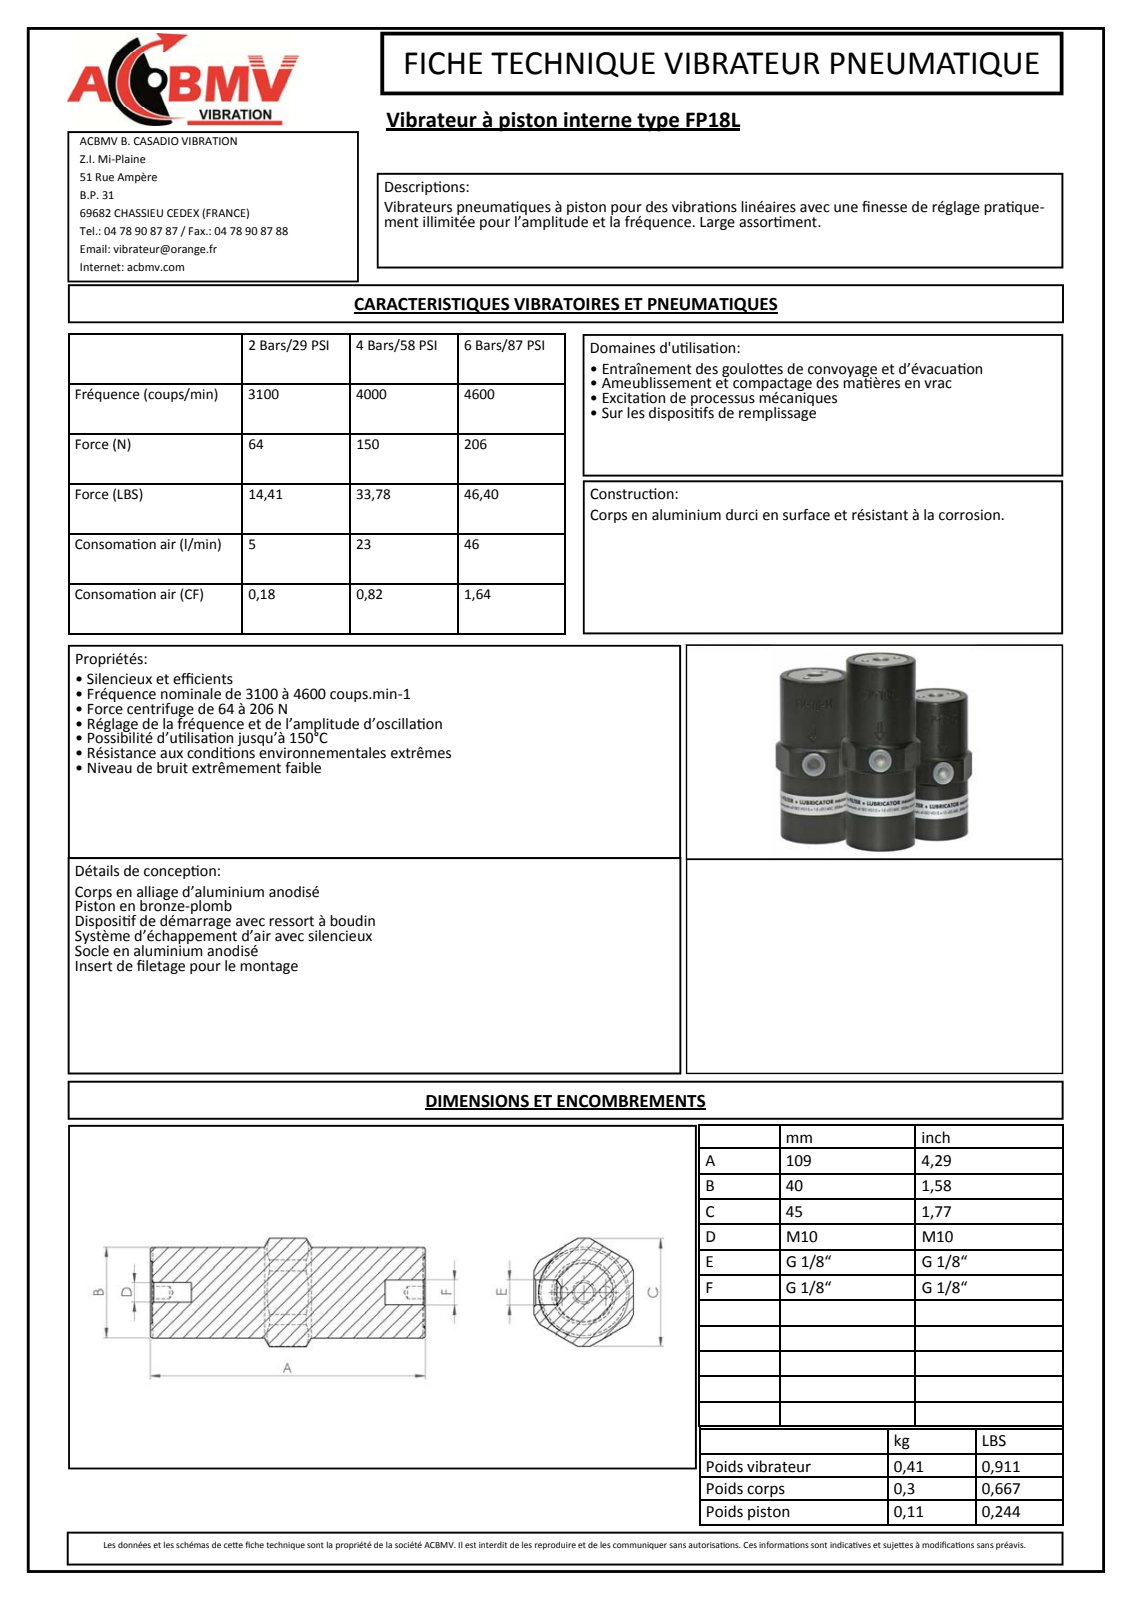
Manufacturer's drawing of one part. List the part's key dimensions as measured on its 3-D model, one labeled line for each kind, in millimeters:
Part name (STEP PRODUCT): 9018-30-M
STEP written by: Autodesk Inventor 2011 (CONFIG_CONTROL_DESIGN)
Units: millimetres
Bodies: 1 solid, 437 faces (177 planar, 58 cylindrical, 202 other)
Overall size (bounding box): 109 × 45.1 × 42
Volume: 137 351 mm³ · Surface area: 18 158 mm²
Round holes (diameter × count): ⌀4.2 ×2, ⌀8.57 ×2, ⌀8.38 ×1
Round bosses / shafts (diameter × count): ⌀40 ×1
Partial cylindrical surfaces — rounded edges, fillets, slot ends (radius × count): R11 ×1, R19.8 ×1, R20.08 ×1, R20.1 ×1, R22.55 ×1
Main face-to-face distances: 42, 108.5, 0.5, 109, 93.3, 92.8, 15.7, 16, 15.5, 77.3
Hole centre spacings: 10, 20
